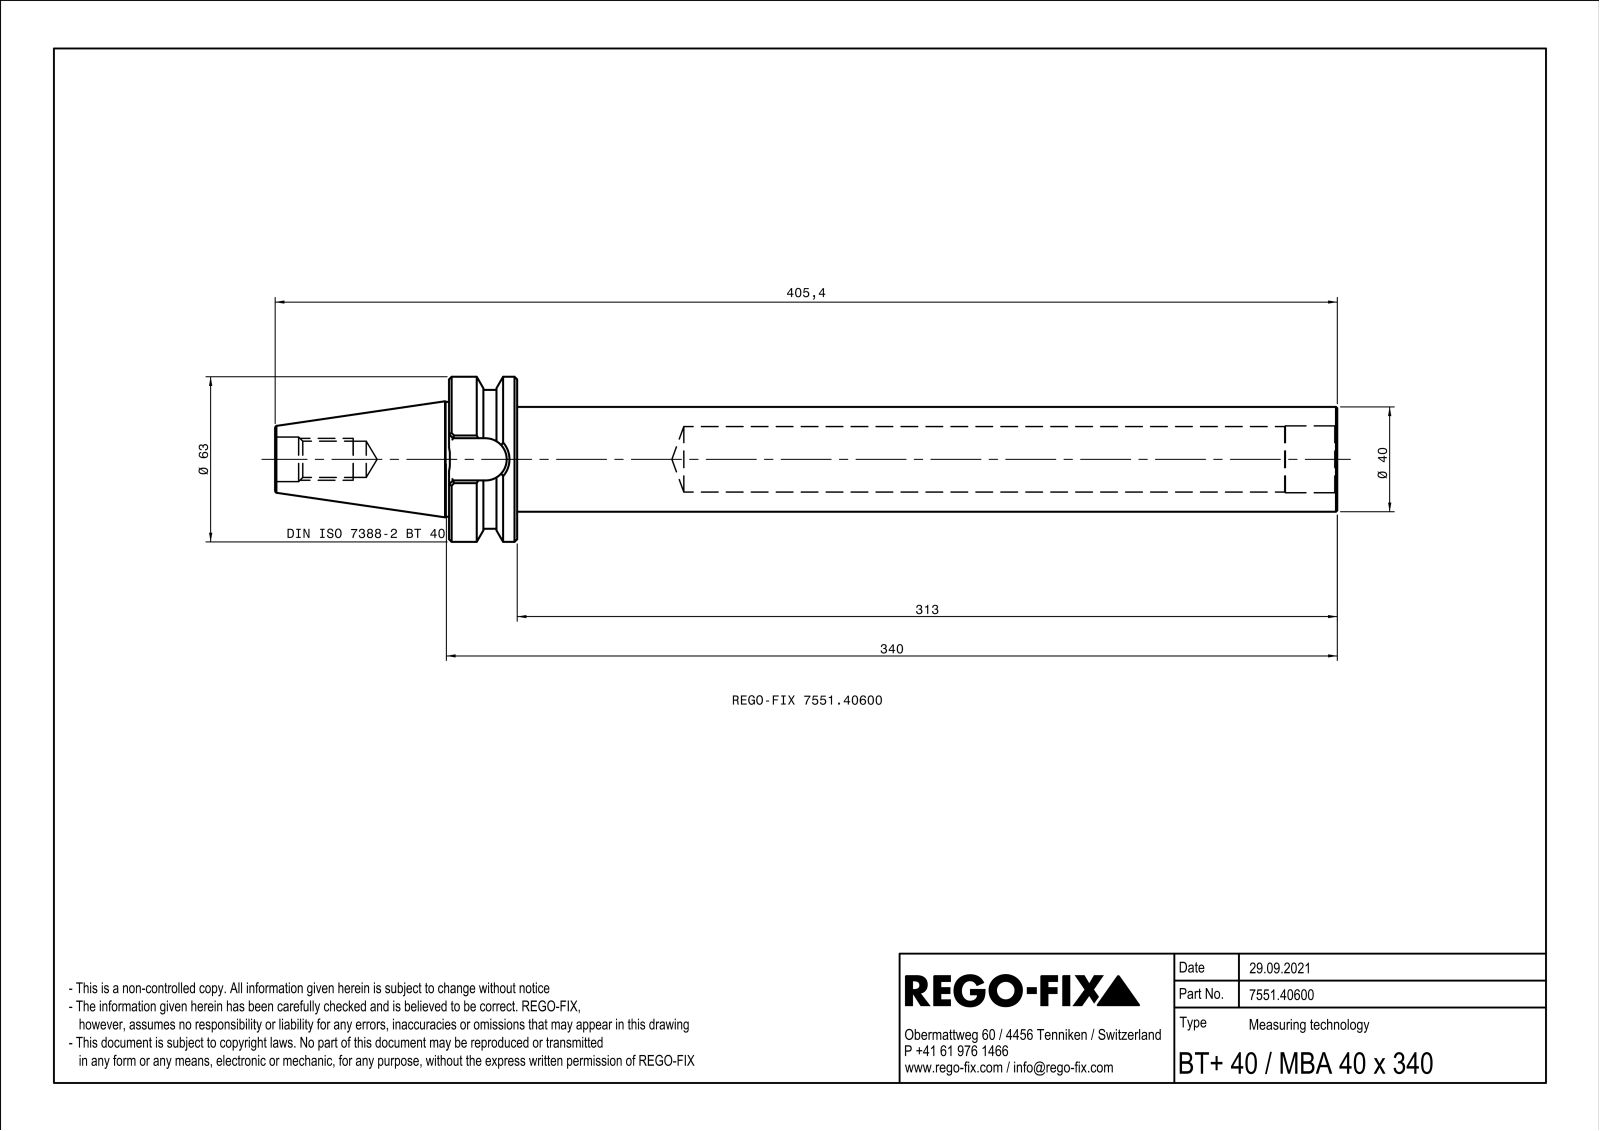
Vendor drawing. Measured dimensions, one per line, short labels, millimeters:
name: NOCUT
written by: SIEMENS PLM Software Solid Edge ST10 (AUTOMOTIVE_DESIGN)
unit: mm
bodies: 1 solid, 85 faces (24 planar, 23 cylindrical, 38 other)
size: 405.4 × 63 × 63
volume: 398 590 mm³; area: 79 048 mm²
holes: 1× ⌀13.81, 1× ⌀13.84, 1× ⌀17, 1× ⌀25, 1× ⌀25.5
bosses: 1× ⌀63, 1× ⌀53, 1× ⌀43.85, 1× ⌀40, 1× ⌀39.4
rounds: 8× R0.5, 1× R8.05
face distances: 26, 313, 339, 45.1, 405.4, 92.4, 66.4, 16.1, 338.7, 25.7
